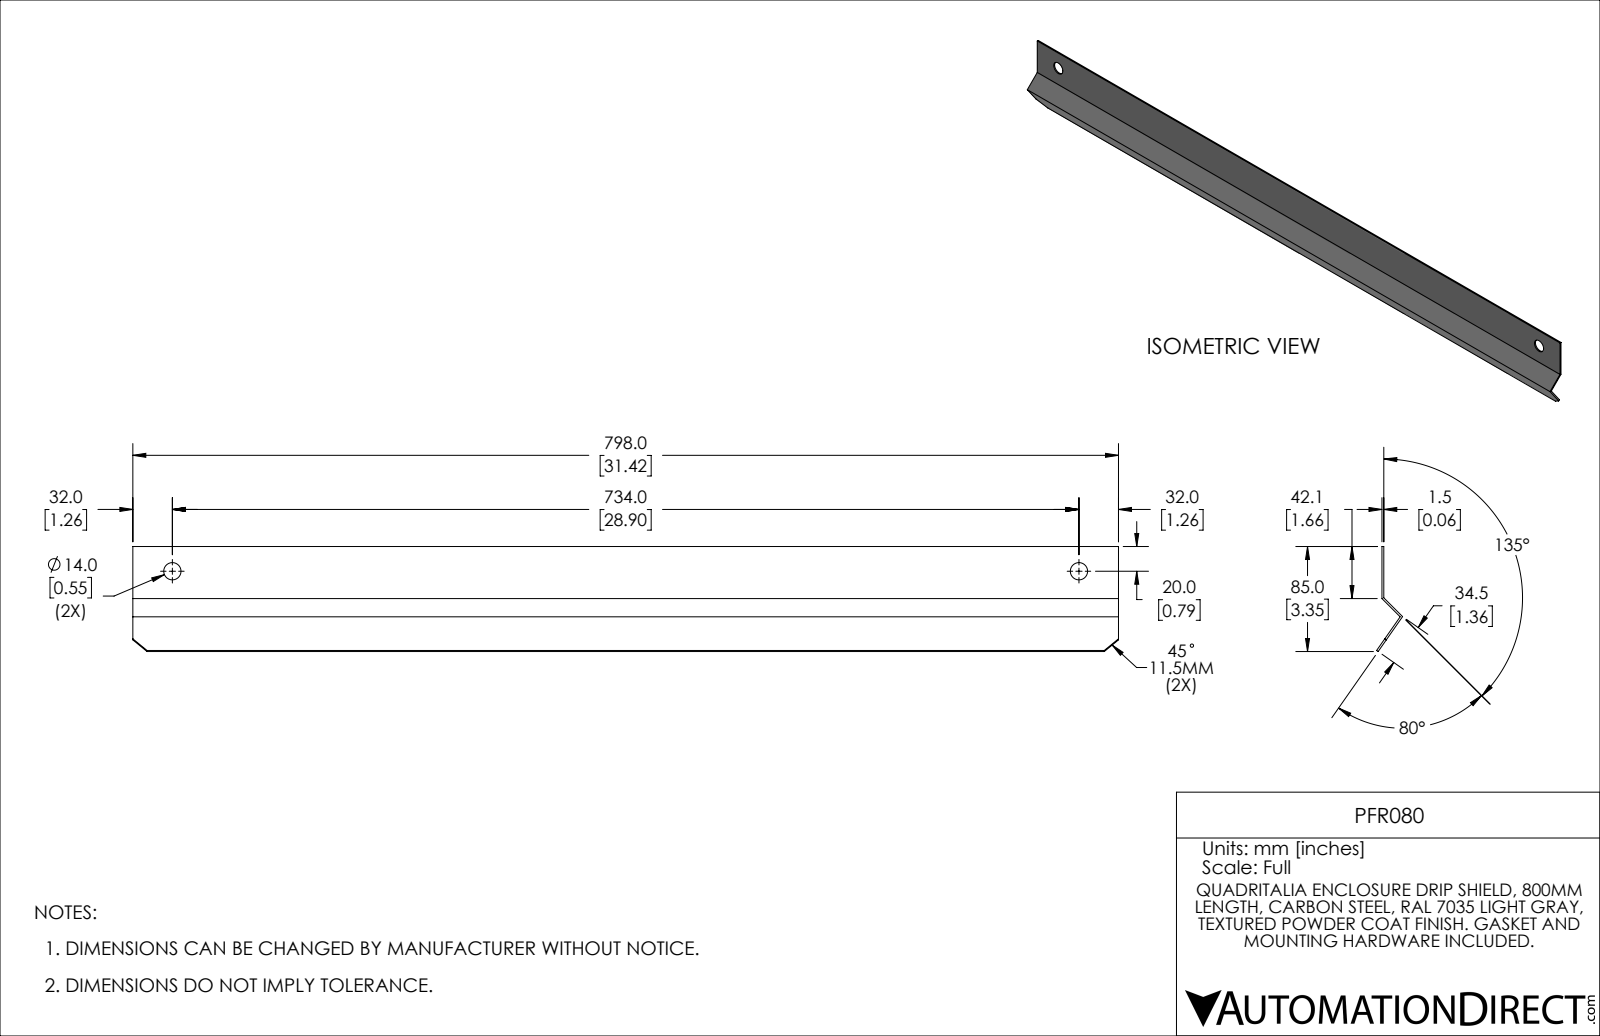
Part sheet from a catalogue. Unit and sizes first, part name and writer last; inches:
Units: inches
Overall size (bounding box): 31.417 × 3.345 × 0.827
Round holes (diameter × count): ⌀0.551 ×2
Main face-to-face distances: 0.059, 31.417
Hole centre spacings: 28.898
Volume: 7.035 in³ · Surface area: 242.6 in²
Bodies: 1 solid, 14 faces (12 planar, 2 cylindrical, 0 other)
Part name (STEP PRODUCT): PFR080
STEP written by: SolidWorks 2021 (CONFIG_CONTROL_DESIGN)
